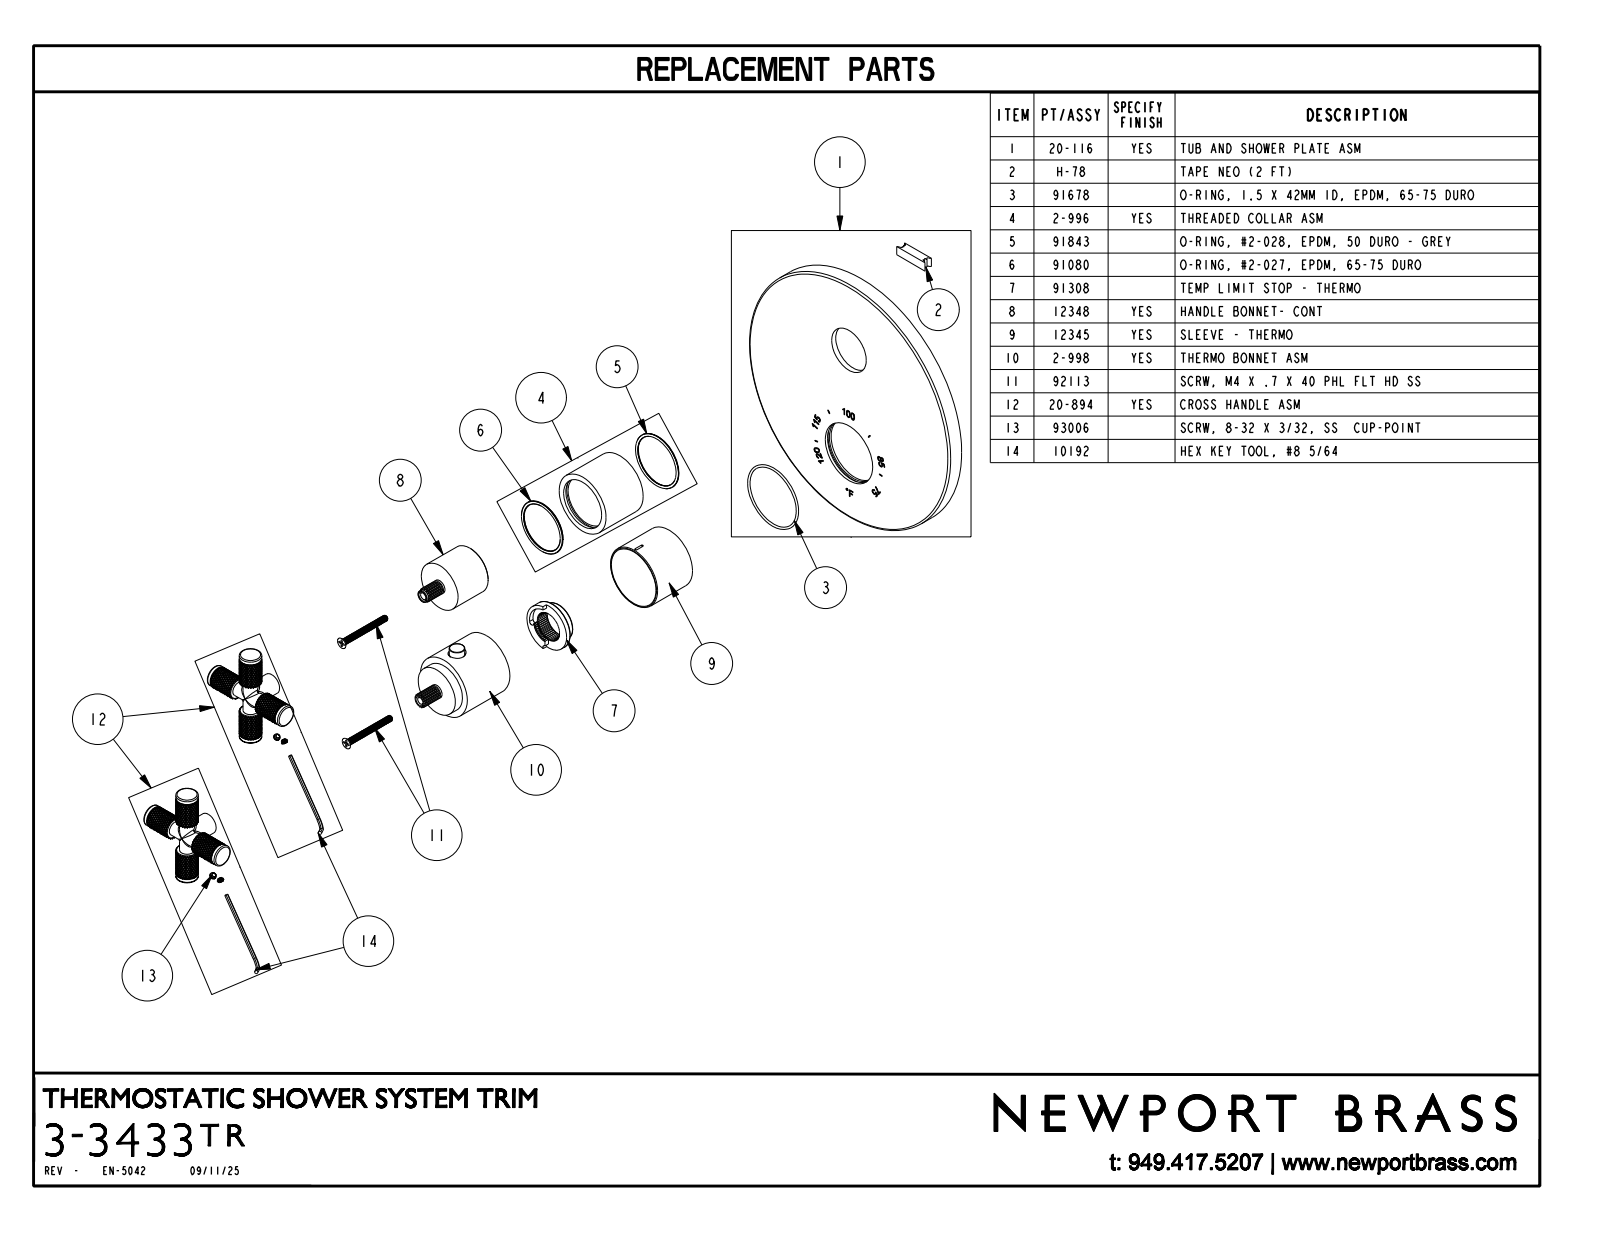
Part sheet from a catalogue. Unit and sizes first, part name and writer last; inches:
Units: inches
Overall size (bounding box): 7.09 × 7.09 × 3.494
Round holes (diameter × count): ⌀0.063 ×1, ⌀0.406 ×1, ⌀1.342 ×1, ⌀1.673 ×1
Round bosses / shafts (diameter × count): ⌀0.563 ×4, ⌀0.562 ×4, ⌀0.375 ×4, ⌀1.654 ×2, ⌀0.55 ×2, ⌀0.37 ×2, ⌀7.09 ×1, ⌀1.31 ×1
Partial cylindrical surfaces — rounded edges, fillets, slot ends (radius × count): R0.039 ×1, R0.756 ×1
Main face-to-face distances: 0.438, 0.358, 0.656, 0.218, 2.41, 1.972, 1.754, 0.028, 0.628, 0.19
Hole centre spacings: 1.142, 3.152, 4.292
Volume: 26.72 in³ · Surface area: 132.3 in²
Bodies: 1 solid, 15398 faces (138 planar, 2875 cylindrical, 12385 other)
Part name (STEP PRODUCT): 3-3433TR
STEP written by: CREO PARAMETRIC BY PTC INC, 2025093 (CONFIG_CONTROL_DESIGN)
